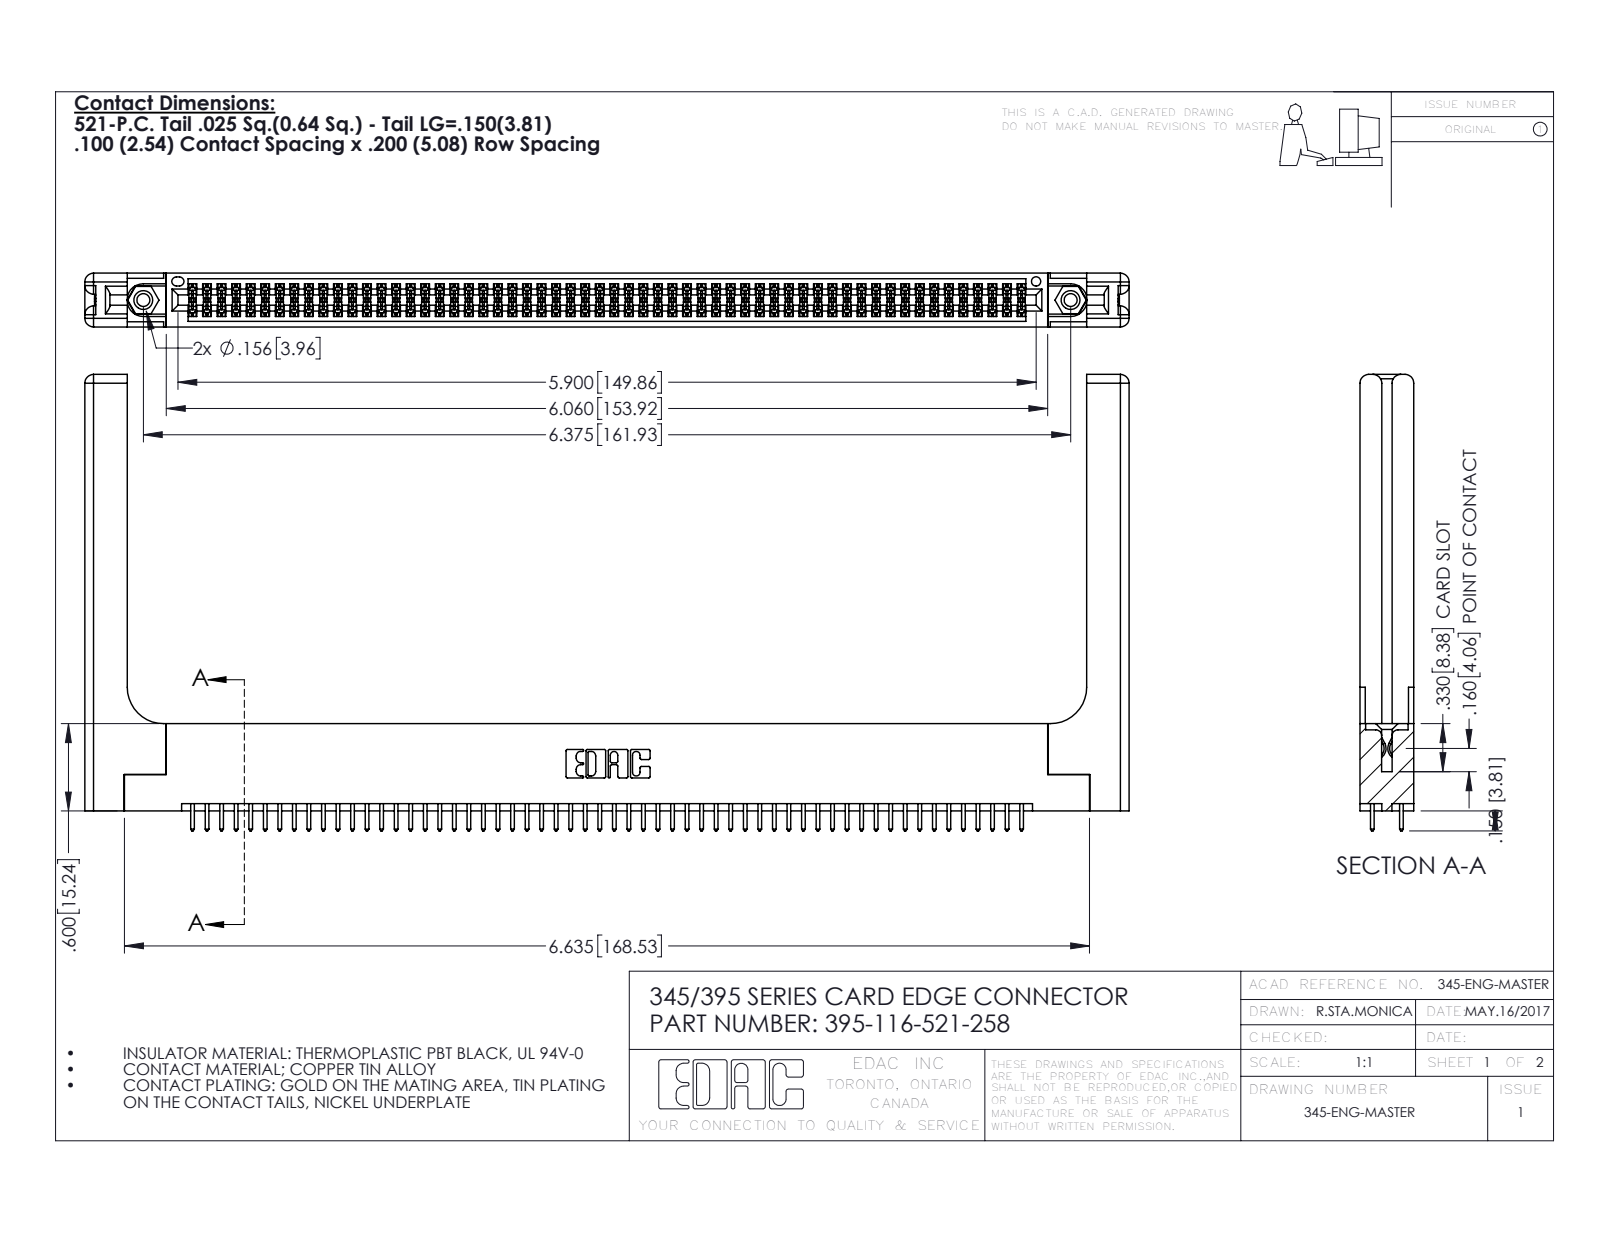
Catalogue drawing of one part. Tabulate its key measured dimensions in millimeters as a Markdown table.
| quantity | value |
| --- | --- |
| part name | 345-250-001_345-250-001-102; 345 Part_Flush Mounting Lugs - 0.156 Dia-TH; 345-292-001_345-293-121; 395-116-521-258 (+1 more) |
| STEP written by | SolidWorks 2016 (CONFIG_CONTROL_DESIGN) |
| units | millimeters |
| bodies | 121 solids, 6182 faces (4056 planar, 2066 cylindrical, 60 other) |
| overall size | 182.3 × 79.7 × 9.4 |
| volume | 26 280 mm³ |
| surface area | 31 390 mm² |
| round holes (diameter × count) | 2.3 × 2, 3.2 × 2, 4 × 2, 1.6 × 1 |
| round bosses / shafts (diameter × count) | 3.9 × 2 |
| partial cylindrical surfaces (radius × count) | 0.2 × 174, 0.3 × 116, 0.3 × 22, 1.5 × 16, 0.2 × 6, 0.8 × 6, 0.7 × 3, 0.4 × 2 |
| main face-to-face distances | 1.8, 7.6, 9.4, 5.1, 2.5, 6.9, 0.6, 5.7, 4.4, 3.8 |
| hole center spacings | 6.9, 155.9, 161.9 |
